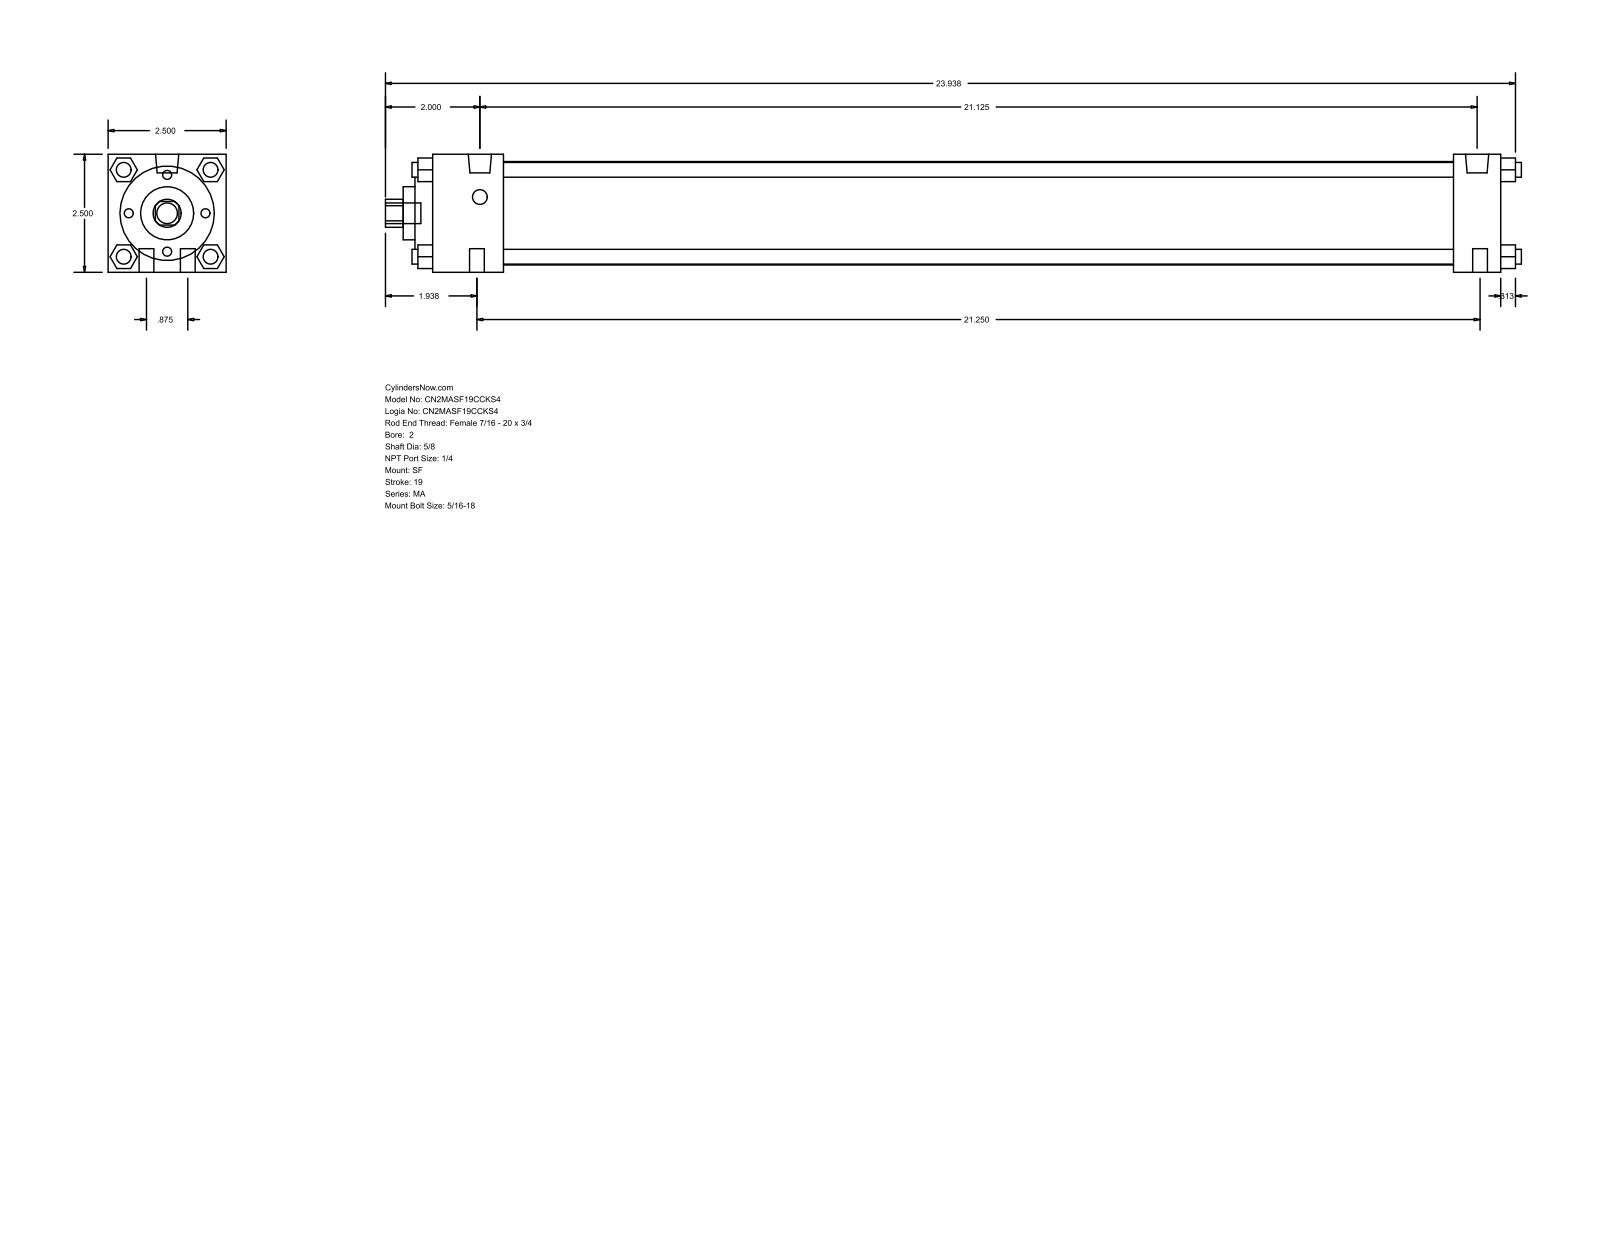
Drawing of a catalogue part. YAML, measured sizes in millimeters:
part_name: "MA_SF__0200_0.625"
step_written_by: "GSSL Pune (CONFIG_CONTROL_DESIGN)"
units: millimeters
bodies: {solids: 0, faces: 126, planar: 95, cylindrical: 31, other: 0}
overall_size: [611.19, 63.5, 63.5]
round_holes:
  - {diameter: 15.88, count: 1}
  - {diameter: 28.57, count: 1}
  - {diameter: 50.8, count: 1}
  - {diameter: 55.63, count: 1}
round_bosses_or_shafts:
  - {diameter: 7.94, count: 10}
  - {diameter: 12.49, count: 2}
  - {diameter: 11.11, count: 1}
partial_cylinders:
  - {radius: 7.54, count: 1}
face_to_face_distances: [63.5, 12.7, 38.1, 9.52, 574.68, 549.27, 25.41, 511.17, 536.58, 47.62]
